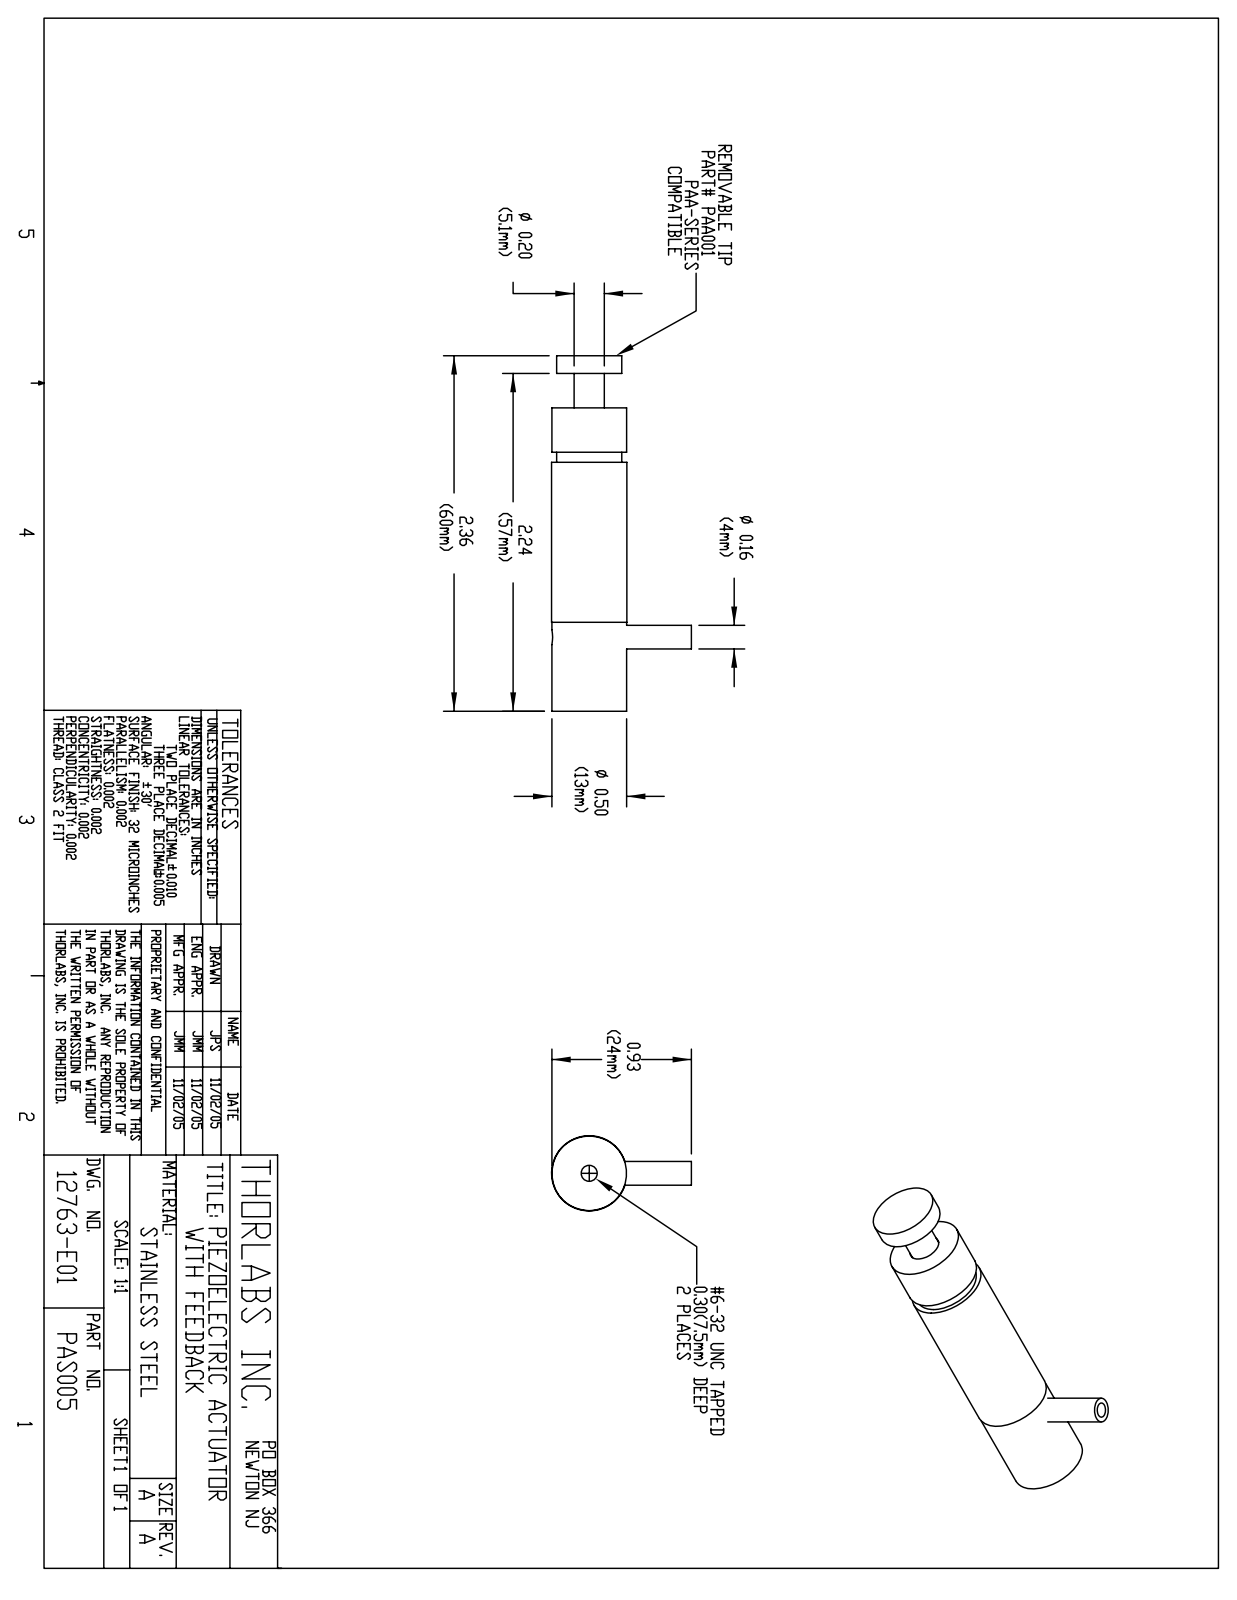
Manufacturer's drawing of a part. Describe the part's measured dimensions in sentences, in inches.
The part is named "12763-E0W". Its 3-D file was written by "SolidWorks 2007 (AUTOMOTIVE_DESIGN)". It is 0 solids with 39 faces: 11 planar, 28 cylindrical and 0 other. Overall it measures 2.362 by 0.928 by 0.5 inches. Round holes: 2 of diameter 0.098, 1 of diameter 0.094, 1 of diameter 0.107, 1 of diameter 0.209, 1 of diameter 0.376, 1 of diameter 0.449. Round bosses or shafts: 1 of diameter 0.5, 1 of diameter 0.496, 1 of diameter 0.433, 1 of diameter 0.201, 1 of diameter 0.157. The main face-to-face distances are 2.016, 0.346, 2.362, 0.118, 0.228, 2.244, 0.591, 1.654, 1.969, 1.85.
